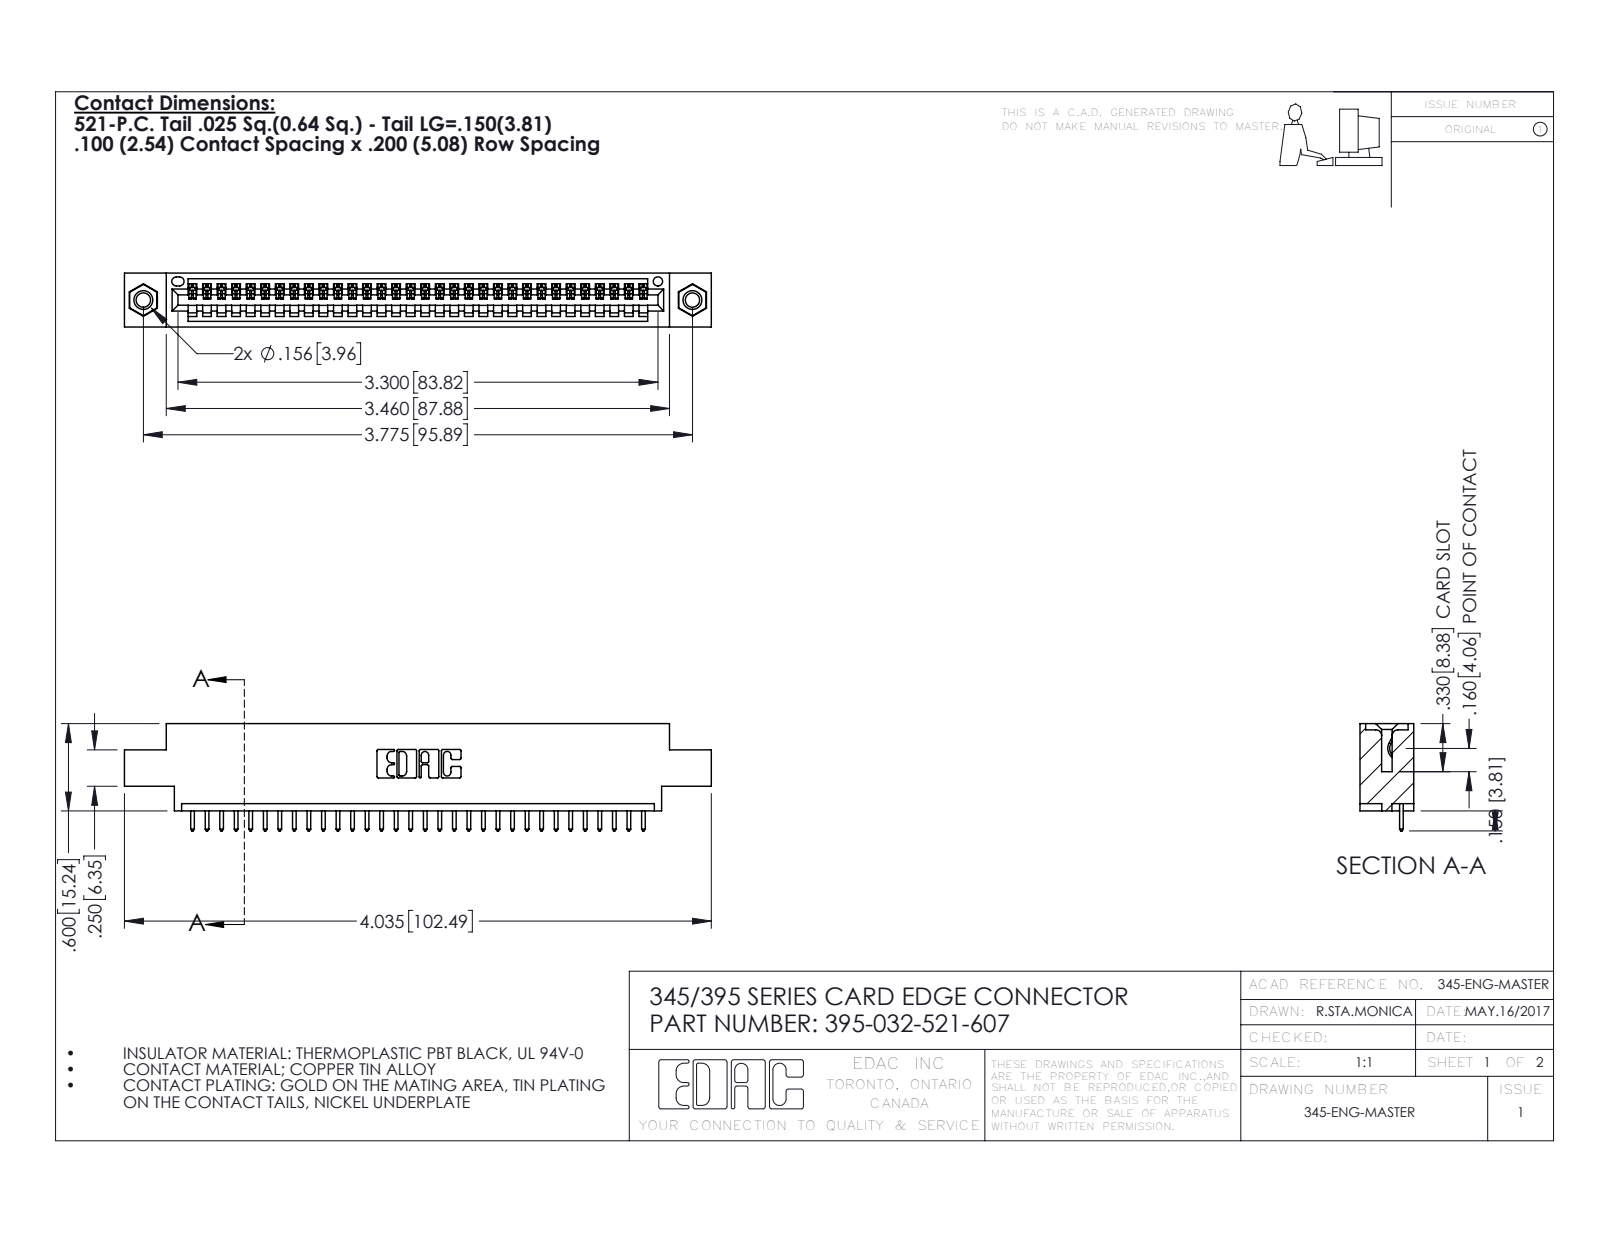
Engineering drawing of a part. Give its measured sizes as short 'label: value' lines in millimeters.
name: 345-250-001_345-250-005-103; 345 Part_0.170 Offset - 0.156 Dia-TI; 395-032-521-607; 345-292-001_345-293-121
written by: SolidWorks 2016 (CONFIG_CONTROL_DESIGN)
unit: mm
bodies: 35 solids, 2046 faces (1396 planar, 634 cylindrical, 16 other)
size: 102.5 × 18.7 × 9.4
volume: 9 440 mm³; area: 12 210 mm²
holes: 2× ⌀2.5, 2× ⌀3.2, 2× ⌀4, 1× ⌀1.6
bosses: 2× ⌀3.9
rounds: 64× R0.2, 64× R0.3, 22× R0.3, 6× R0.2, 6× R0.8, 3× R0.7, 2× R0.8, 2× R1
face distances: 1.8, 7.6, 9.4, 5.1, 2.5, 6.9, 0.6, 5.7, 4.4, 3.8
hole spacings: 6.9, 89.9, 95.9
